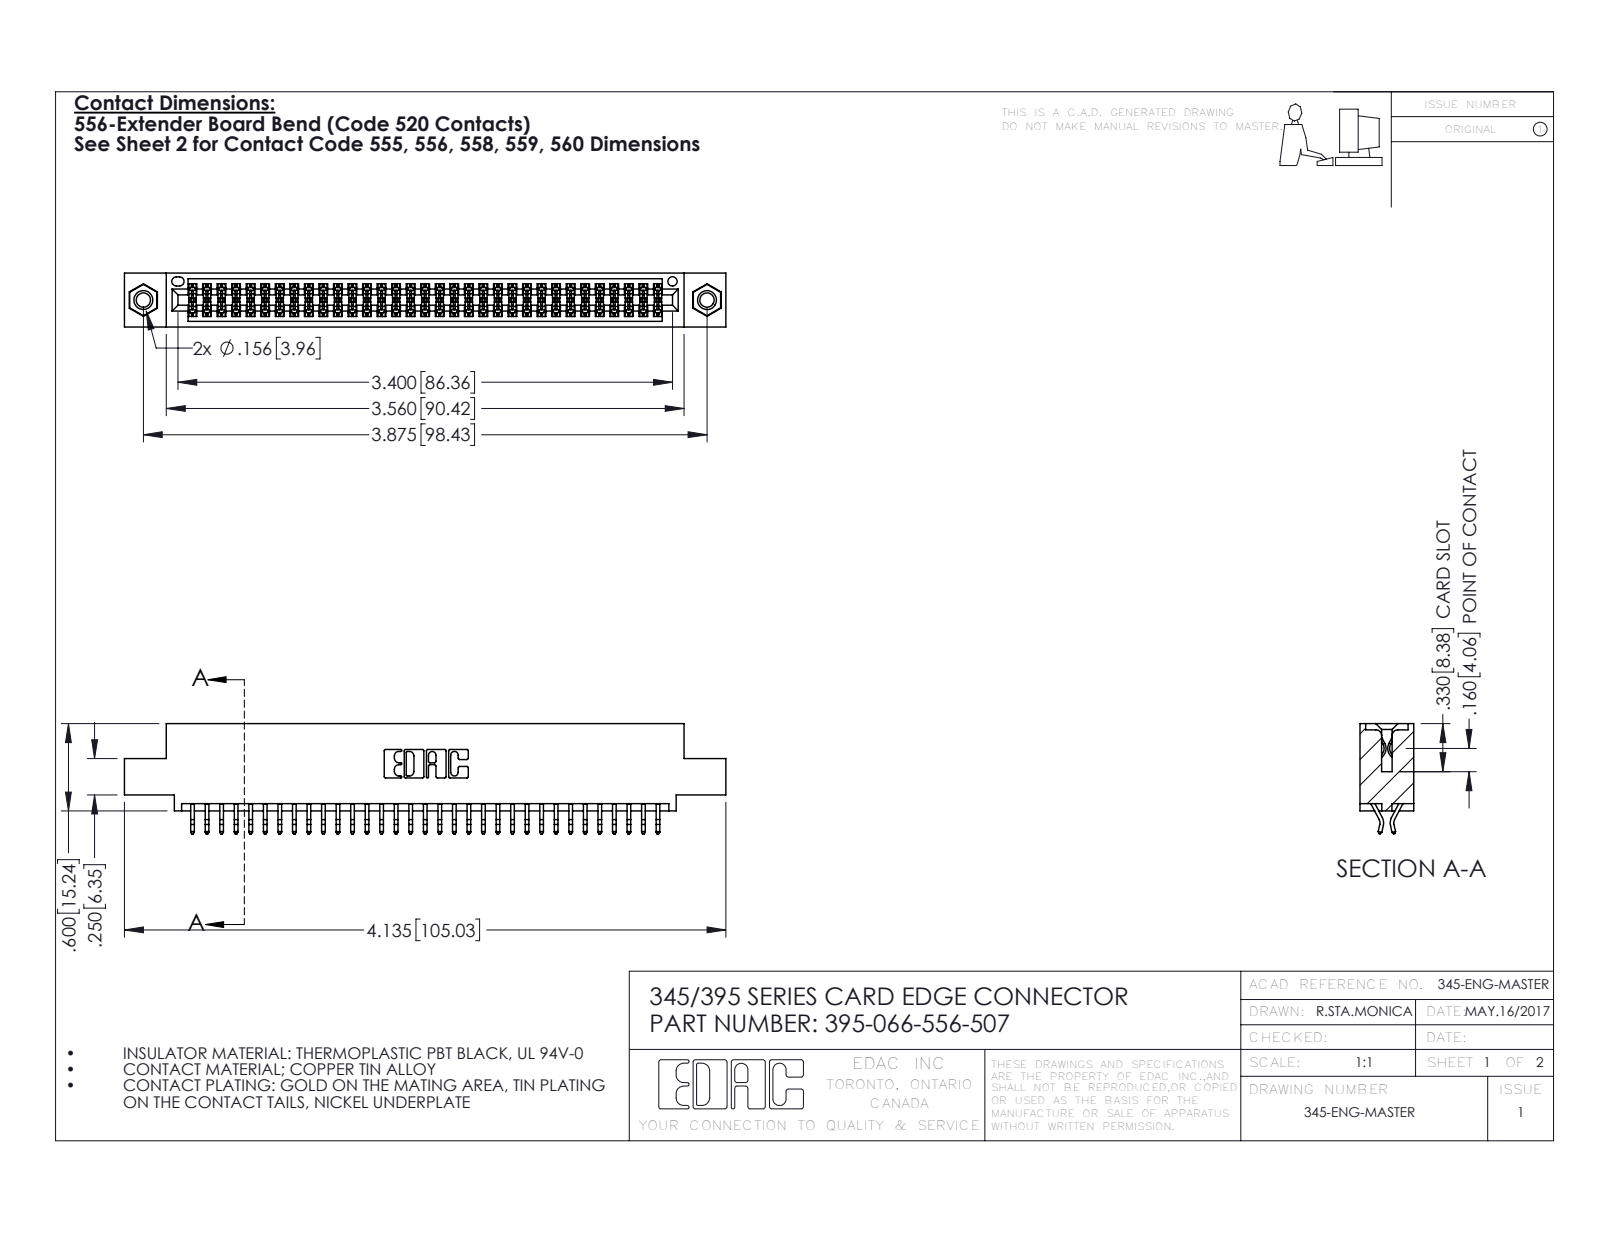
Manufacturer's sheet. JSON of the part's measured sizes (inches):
{"part_name": "395-066-556-507; 345 Part_0.110 Offset - 0.156 Dia-TI; 345-292-001_556 Tail; 345-250-001_345-250-005-103", "step_written_by": "SolidWorks 2016 (CONFIG_CONTROL_DESIGN)", "units": "inches", "bodies": {"solids": 69, "faces": 3886, "planar": 2558, "cylindrical": 1312, "other": 16}, "overall_size": [4.135, 0.757, 0.37], "volume_in3": 0.612, "surface_area_in2": 22.81, "round_holes": [[0.098, 2], [0.125, 2], [0.156, 2], [0.064, 1]], "round_bosses_or_shafts": [[0.155, 2]], "partial_cylinders_radius": [[0.006, 99], [0.01, 22], [0.007, 6], [0.031, 6], [0.026, 3], [0.01, 2], [0.014, 2], [0.019, 2]], "face_to_face_distances": [0.072, 0.298, 0.2, 0.37, 0.025, 0.098, 0.272, 0.225, 0.175, 0.149], "hole_center_spacings": [0.27, 3.64, 3.875]}
